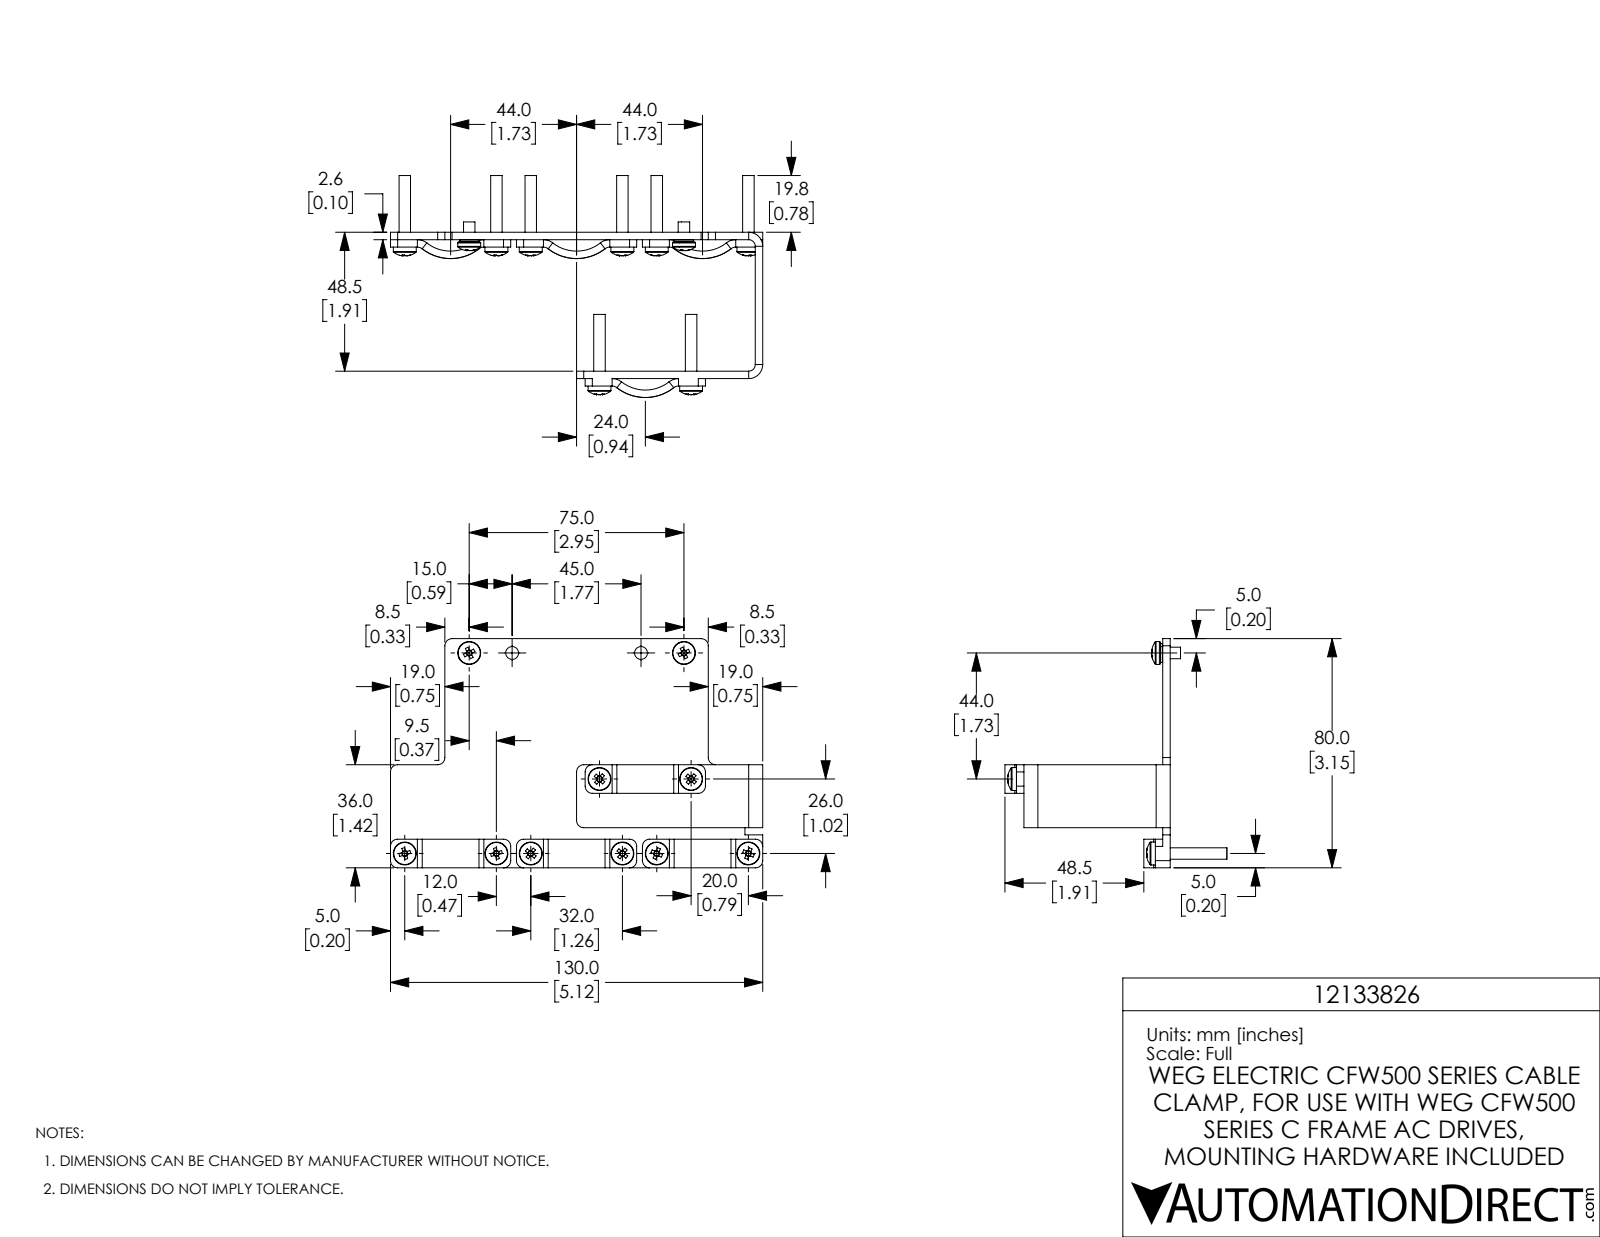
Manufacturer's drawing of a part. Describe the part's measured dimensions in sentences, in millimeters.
The part is named "ZBC_10006124415 nc cmb1". Its 3-D file was written by "SolidWorks 2017 (AUTOMOTIVE_DESIGN)". It is 1 solid with 557 faces: 270 planar, 147 cylindrical and 140 other. Overall it measures 130 by 80 by 77.5 millimeters. Its volume is 36 380 cubic millimeters and its surface area 30 500 square millimeters. Round holes: 10 of diameter 4.5, 2 of diameter 3.3, 2 of diameter 3.8. Round bosses or shafts: 10 of diameter 8, 10 of diameter 4, 2 of diameter 6.6, 2 of diameter 3.2. Partial cylindrical surfaces (rounded edges, fillets, slot ends): 23 of radius 2.5, 8 of radius 2.7, 8 of radius 5.3, 4 of radius 13.5, 4 of radius 16.1, 2 of radius 2.3, 2 of radius 4.9. The main face-to-face distances are 2.6, 48.5, 45.9, 51.1, 36, 26, 10, 5.2, 22, 14. The hole center spacings are 32, 44, 12, 15, 32.8, 35.4, 60, 70.2.
